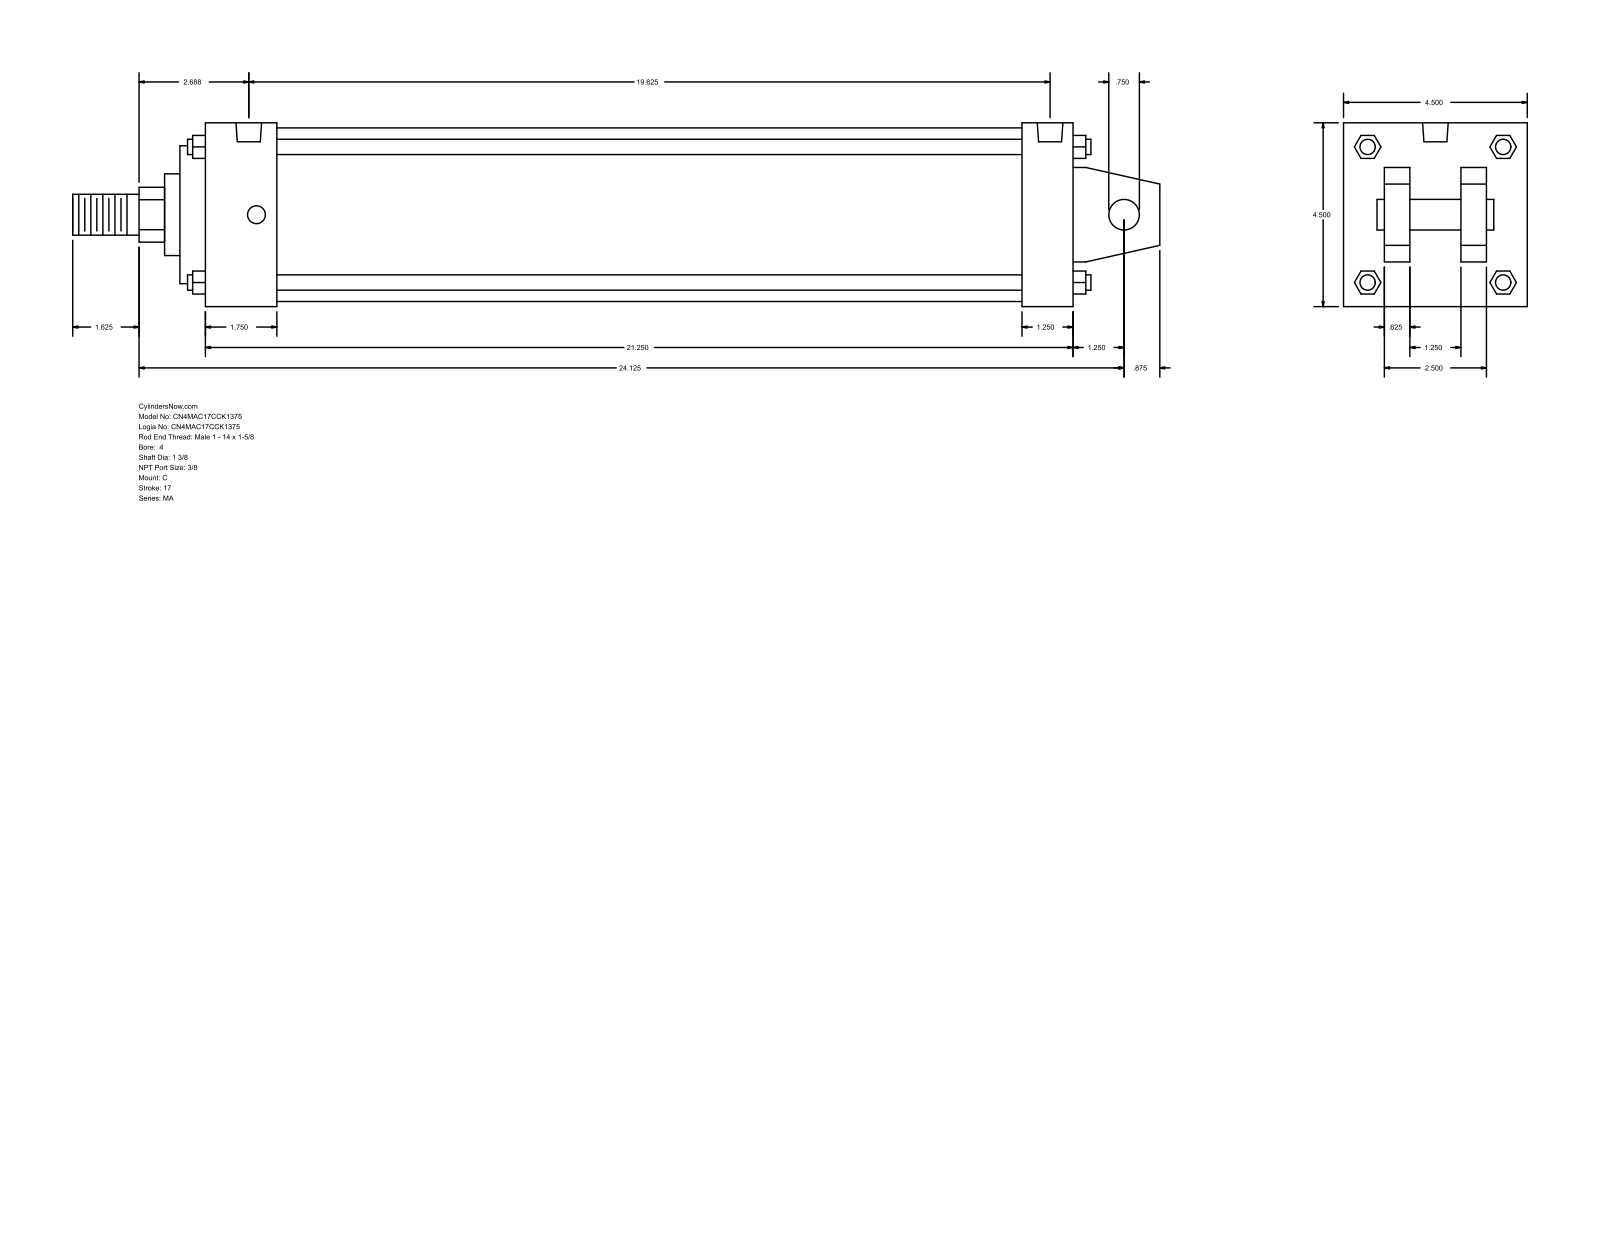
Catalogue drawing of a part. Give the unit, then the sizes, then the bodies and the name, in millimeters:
Units: millimetres
Overall size (bounding box): 676.27 × 114.3 × 114.3
Round holes (diameter × count): ⌀11.11 ×4, ⌀15.93 ×2
Round bosses / shafts (diameter × count): ⌀9.53 ×4, ⌀107.95 ×1, ⌀85.72 ×1, ⌀50.8 ×1, ⌀34.92 ×1, ⌀25.4 ×1, ⌀19.05 ×1
Partial cylindrical surfaces — rounded edges, fillets, slot ends (radius × count): R17.06 ×1
Main face-to-face distances: 114.3, 15.87, 539.75, 73.03, 41.27, 25.4, 88.9, 47.63, 555.62, 523.87
Hole centre spacings: 488.95, 4.76, 4.77, 493.71, 493.72, 498.48
Bodies: 0 solids, 141 faces (109 planar, 32 cylindrical, 0 other)
Part name (STEP PRODUCT): MA_C__0400_1.375
STEP written by: GSSL Pune (CONFIG_CONTROL_DESIGN)
